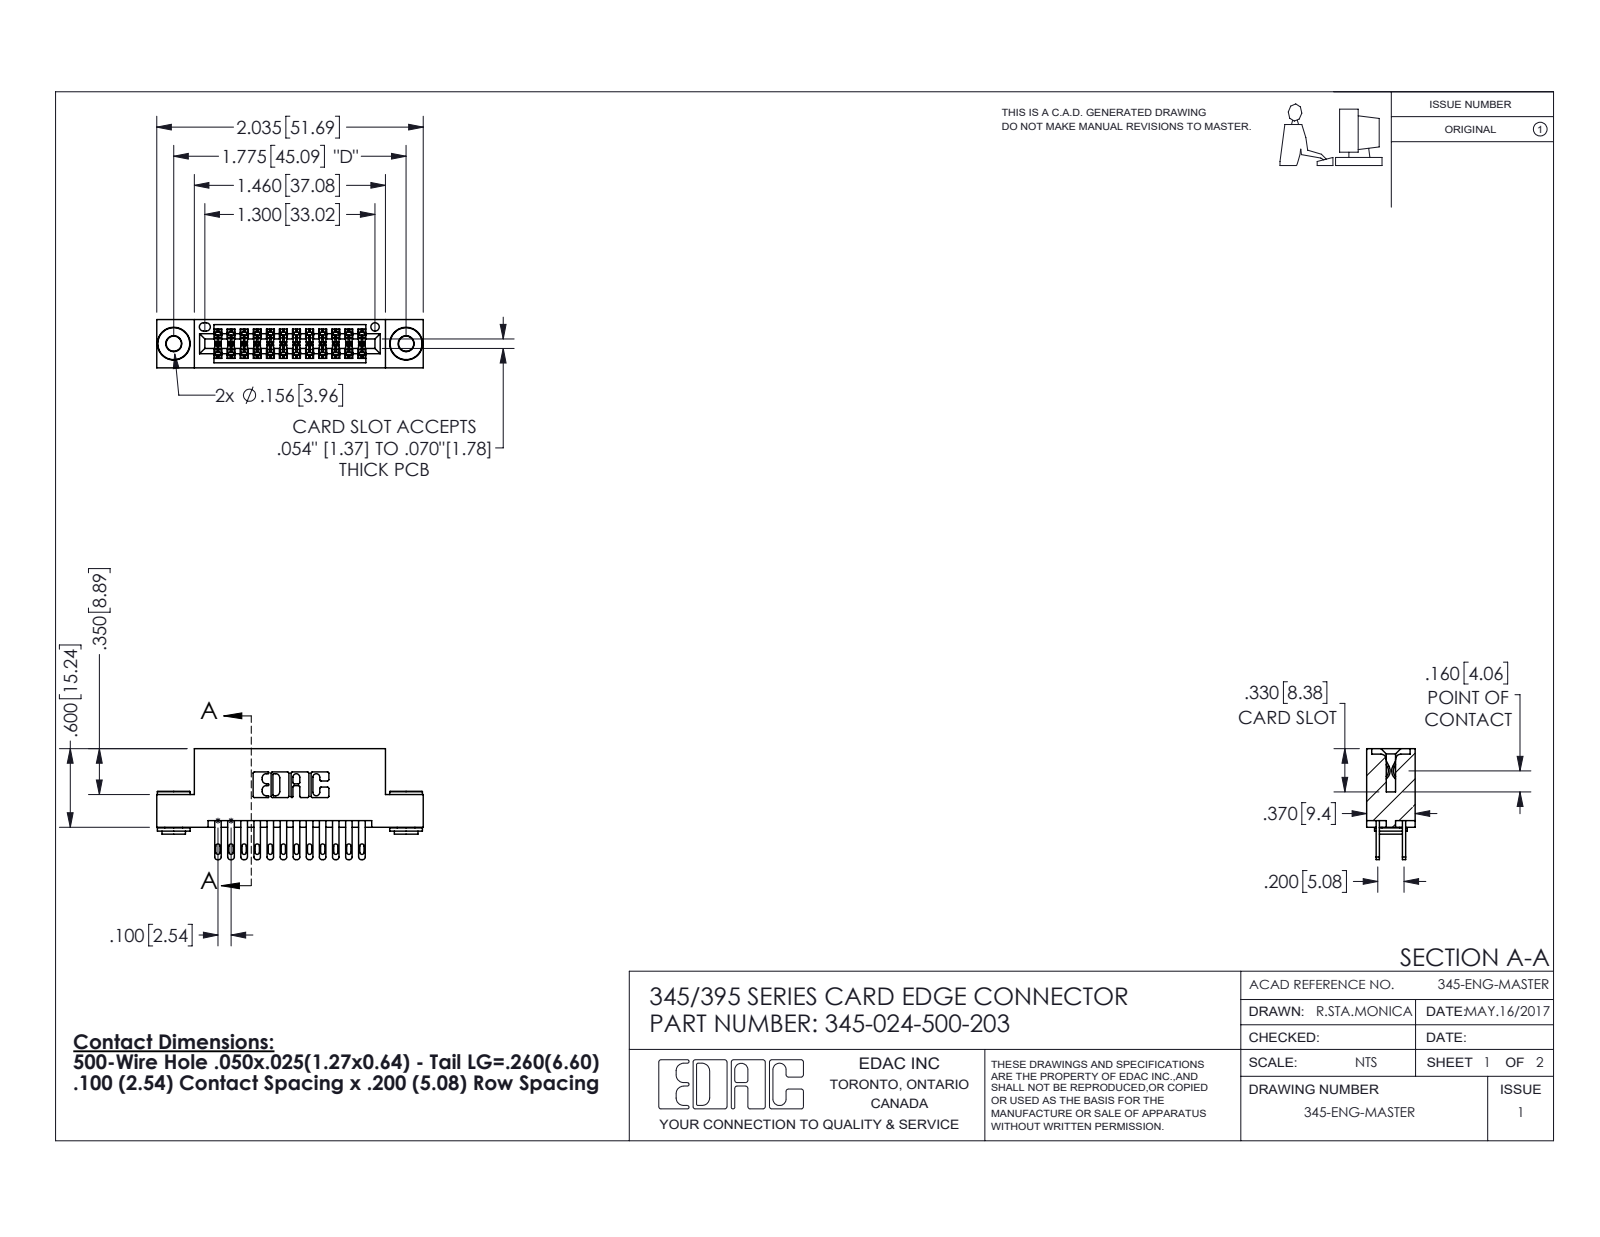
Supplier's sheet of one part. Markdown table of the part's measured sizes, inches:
| quantity | value |
| --- | --- |
| part name | 345-250-002_345-250-002-102; 345-024-500-203; 345-292-001_345-293-100; 345 Part_Flush Mounting Lugs - 0.156 Dia-TH |
| STEP written by | SolidWorks 2016 (CONFIG_CONTROL_DESIGN) |
| units | inches |
| bodies | 27 solids, 1268 faces (738 planar, 522 cylindrical, 8 other) |
| overall size | 2.035 × 0.847 × 0.37 |
| volume | 0.295 in³ |
| surface area | 10.88 in² |
| round holes (diameter × count) | 0.116 × 2, 0.156 × 2, 0.064 × 1 |
| round bosses / shafts (diameter × count) | 0.25 × 2, 0.18 × 2, 0.136 × 2 |
| partial cylindrical surfaces (radius × count) | 0.006 × 36, 0.016 × 24, 0.02 × 24, 0.01 × 22, 0.007 × 6, 0.031 × 6, 0.026 × 3, 0.014 × 2 |
| main face-to-face distances | 0.2, 0.072, 0.298, 0.025, 0.098, 0.272, 0.37, 0.225, 0.1, 0.175 |
| hole center spacings | 0.27, 1.543, 1.775 |
